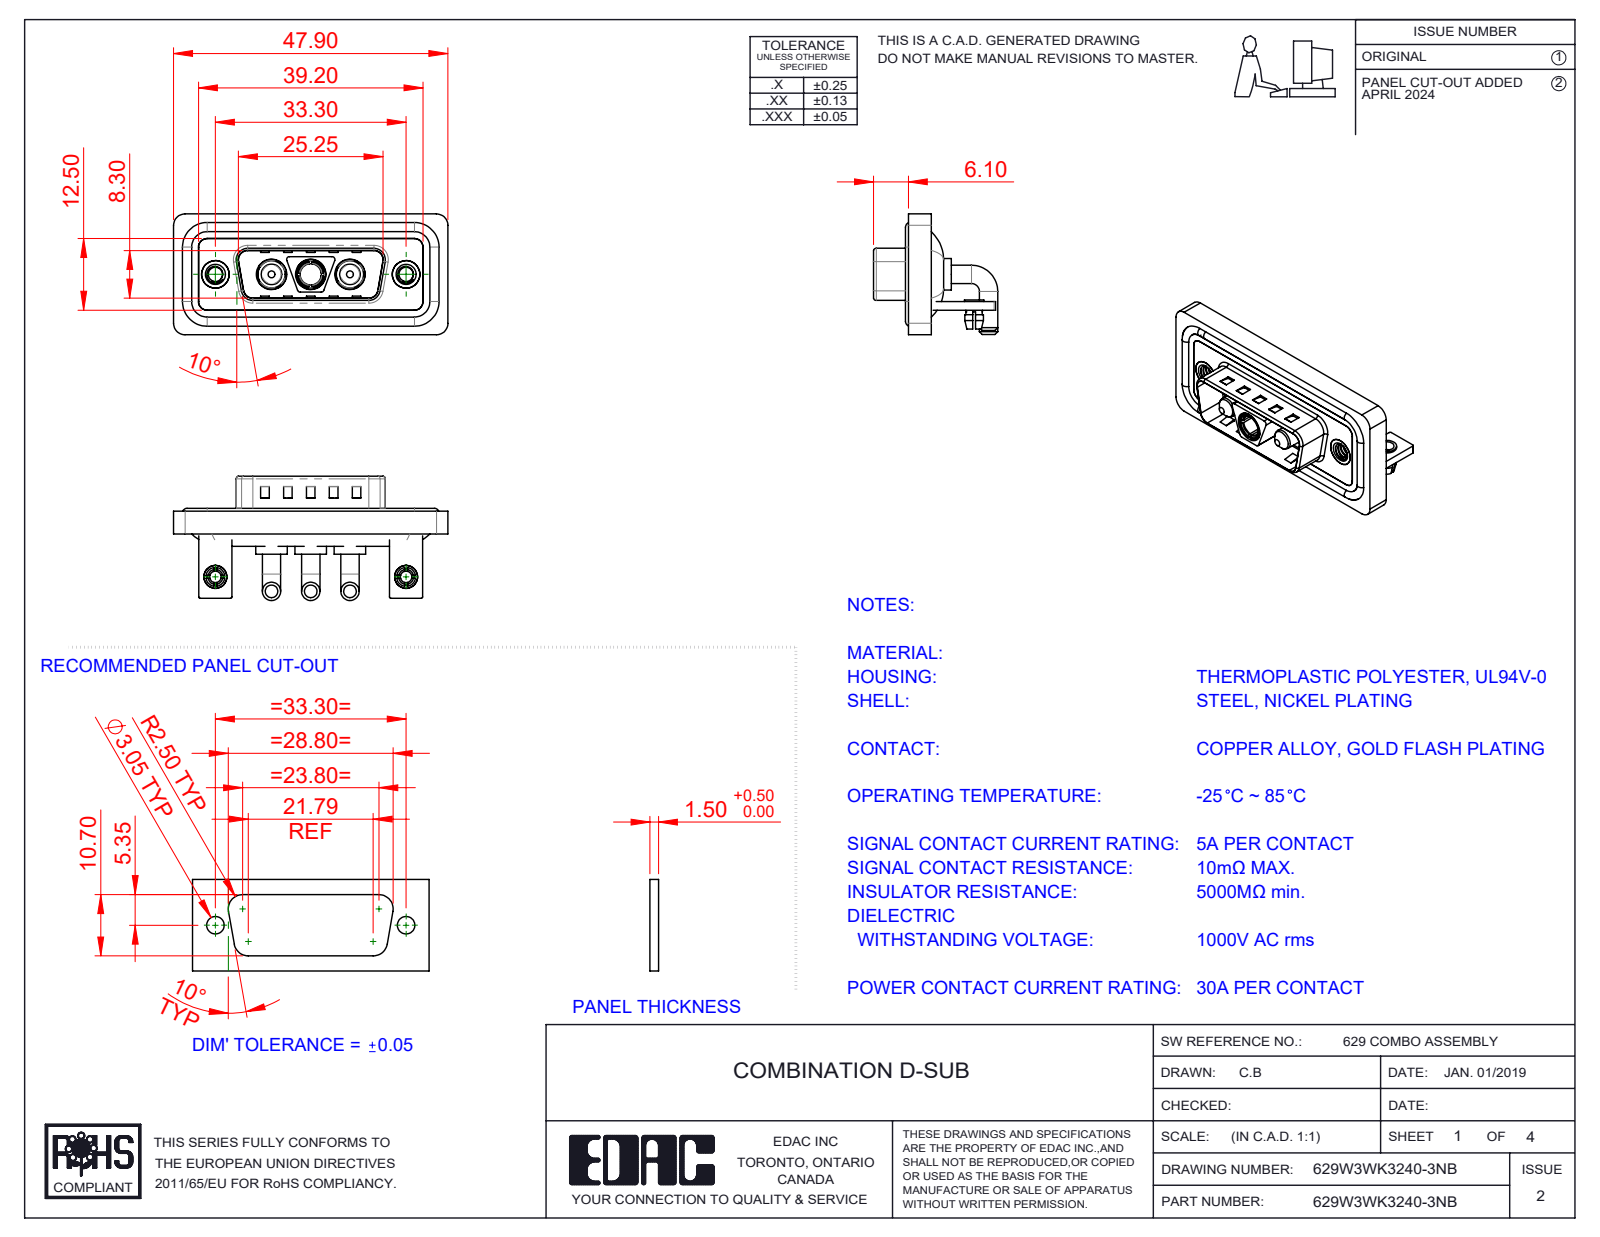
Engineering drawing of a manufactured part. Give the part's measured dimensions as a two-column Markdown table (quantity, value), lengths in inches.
| quantity | value |
| --- | --- |
| part name | 629Combo Shell Rear_15 Contacts; Power Socket_30A RA; 629Combo Waterproof Housing_15 Contacts; 629W3WK3240-3NB (+6 more) |
| STEP written by | SolidWorks 2023 (CONFIG_CONTROL_DESIGN) |
| units | inches |
| bodies | 17 solids, 751 faces (299 planar, 306 cylindrical, 146 other) |
| overall size | 1.886 × 0.854 × 0.831 |
| volume | 0.383 in³ |
| surface area | 15.92 in² |
| round holes (diameter × count) | 0.098 × 4, 0.191 × 3, 0.209 × 3, 0.079 × 2, 0.126 × 2, 0.157 × 2, 0.189 × 2, 0.197 × 2, 0.146 × 1 |
| round bosses / shafts (diameter × count) | 0.126 × 6, 0.063 × 4, 0.217 × 3, 0.205 × 3, 0.187 × 3, 0.148 × 3, 0.193 × 2, 0.157 × 2 |
| partial cylindrical surfaces (radius × count) | 0.079 × 21, 0.059 × 18, 0.01 × 16, 0.02 × 13, 0.063 × 8, 0.024 × 4, 0.026 × 4, 0.035 × 4 |
| main face-to-face distances | 0.016, 0.059, 0.031, 0.114, 0.043, 0.083, 0.146, 0.063, 0.047, 0.177 |
| hole center spacings | 0.27, 0.386, 0.656, 0.925, 1.311, 0.539 |
